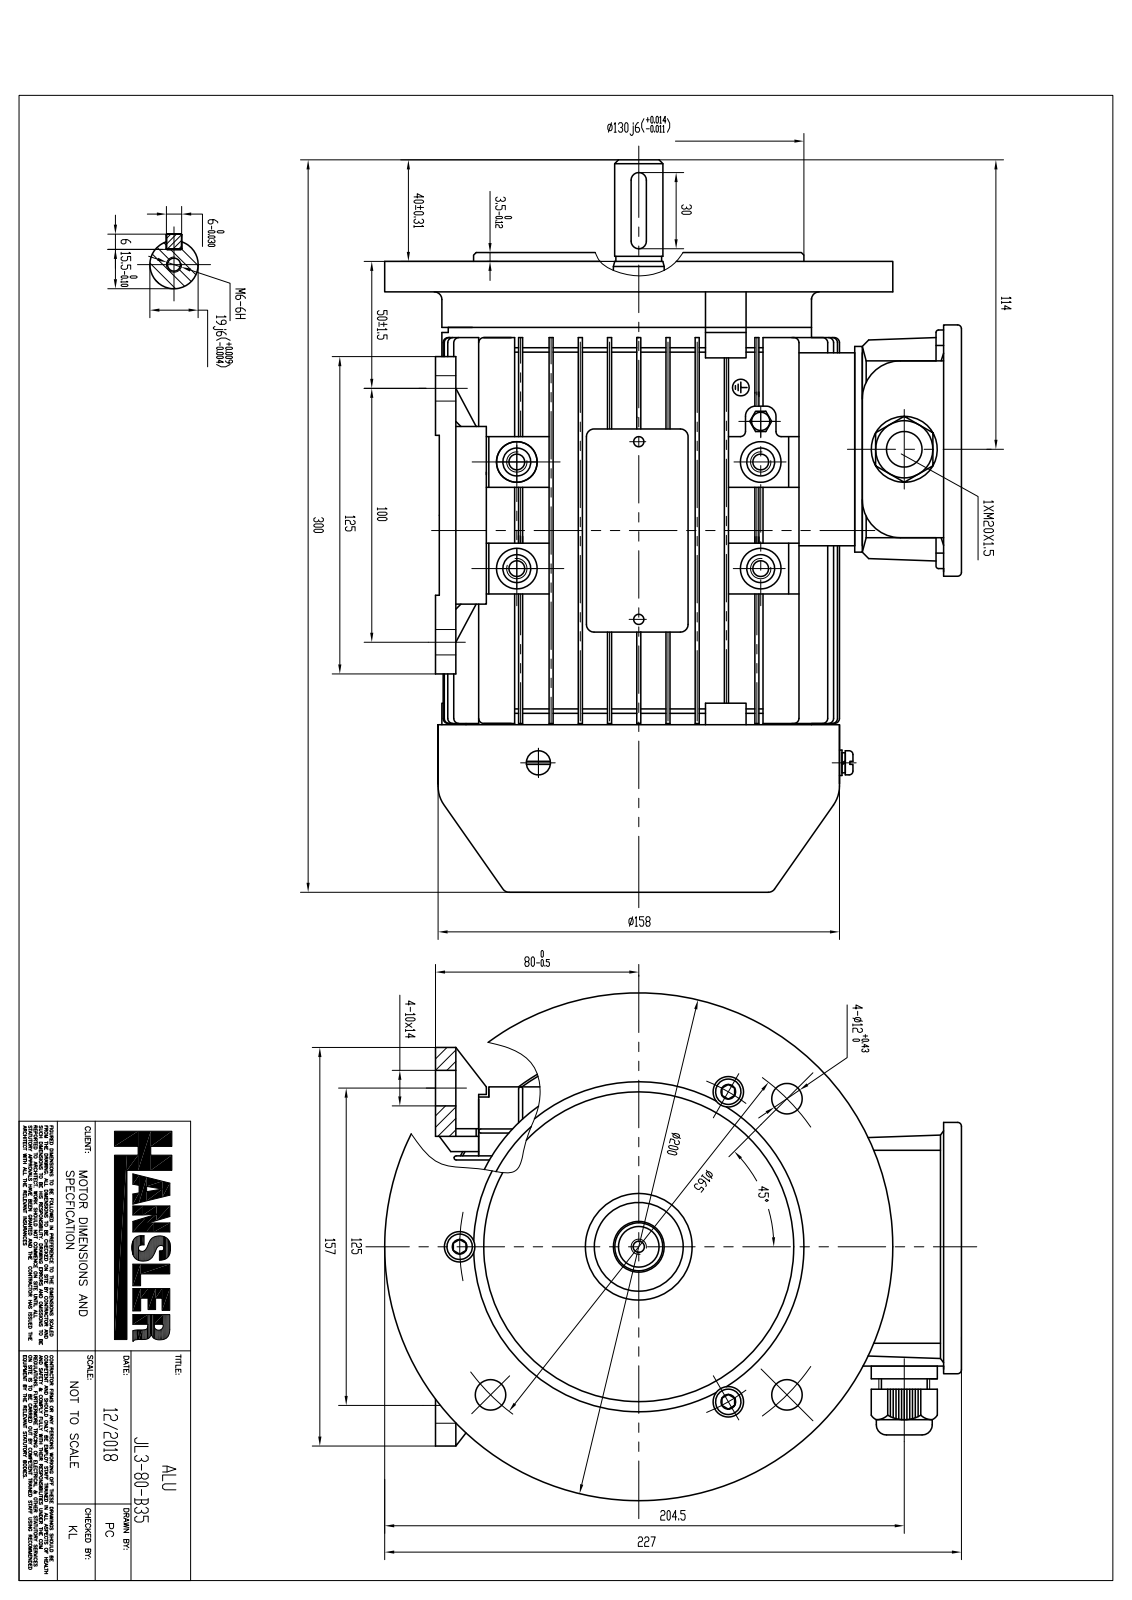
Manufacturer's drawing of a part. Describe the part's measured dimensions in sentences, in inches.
The part is named "JL3-80-B35". Its 3-D file was written by "DATAKIT 2018 (c) (AP242_MANAGED_MODEL_BASED_3D_ENGINEERING_MIM_LF)". It is 45 solids with 2574 faces: 1268 planar, 778 cylindrical and 528 other. Overall it measures 11.378 by 9.083 by 7.874 inches. Its volume is 79.76 cubic inches and its surface area 1 116 square inches. Round holes: 13 of diameter 0.157, 11 of diameter 0.472, 10 of diameter 0.63, 8 of diameter 0.26, 4 of diameter 0.207, 4 of diameter 0.209, 4 of diameter 0.228, 4 of diameter 0.354, 3 of diameter 0.252, 3 of diameter 0.276, 2 of diameter 0.079, 2 of diameter 0.378. Round bosses or shafts: 8 of diameter 0.433, 7 of diameter 0.394, 5 of diameter 0.709, 4 of diameter 0.591, 4 of diameter 0.512, 4 of diameter 0.472, 4 of diameter 0.315, 4 of diameter 0.309. Partial cylindrical surfaces (rounded edges, fillets, slot ends): 84 of radius 0.079, 72 of radius 0.039, 31 of radius 0.118, 26 of radius 0.157, 24 of radius 0.013, 20 of radius 0.197, 16 of radius 0.012, 12 of radius 0.015. The main face-to-face distances are 0.063, 0.453, 0.906, 1.358, 0.416, 1.811, 0.39, 0.516, 0.832, 0.843. The hole center spacings are 0.557, 1.654, 2.126, 3.425, 3.78, 4.126, 1.916, 2.776.
